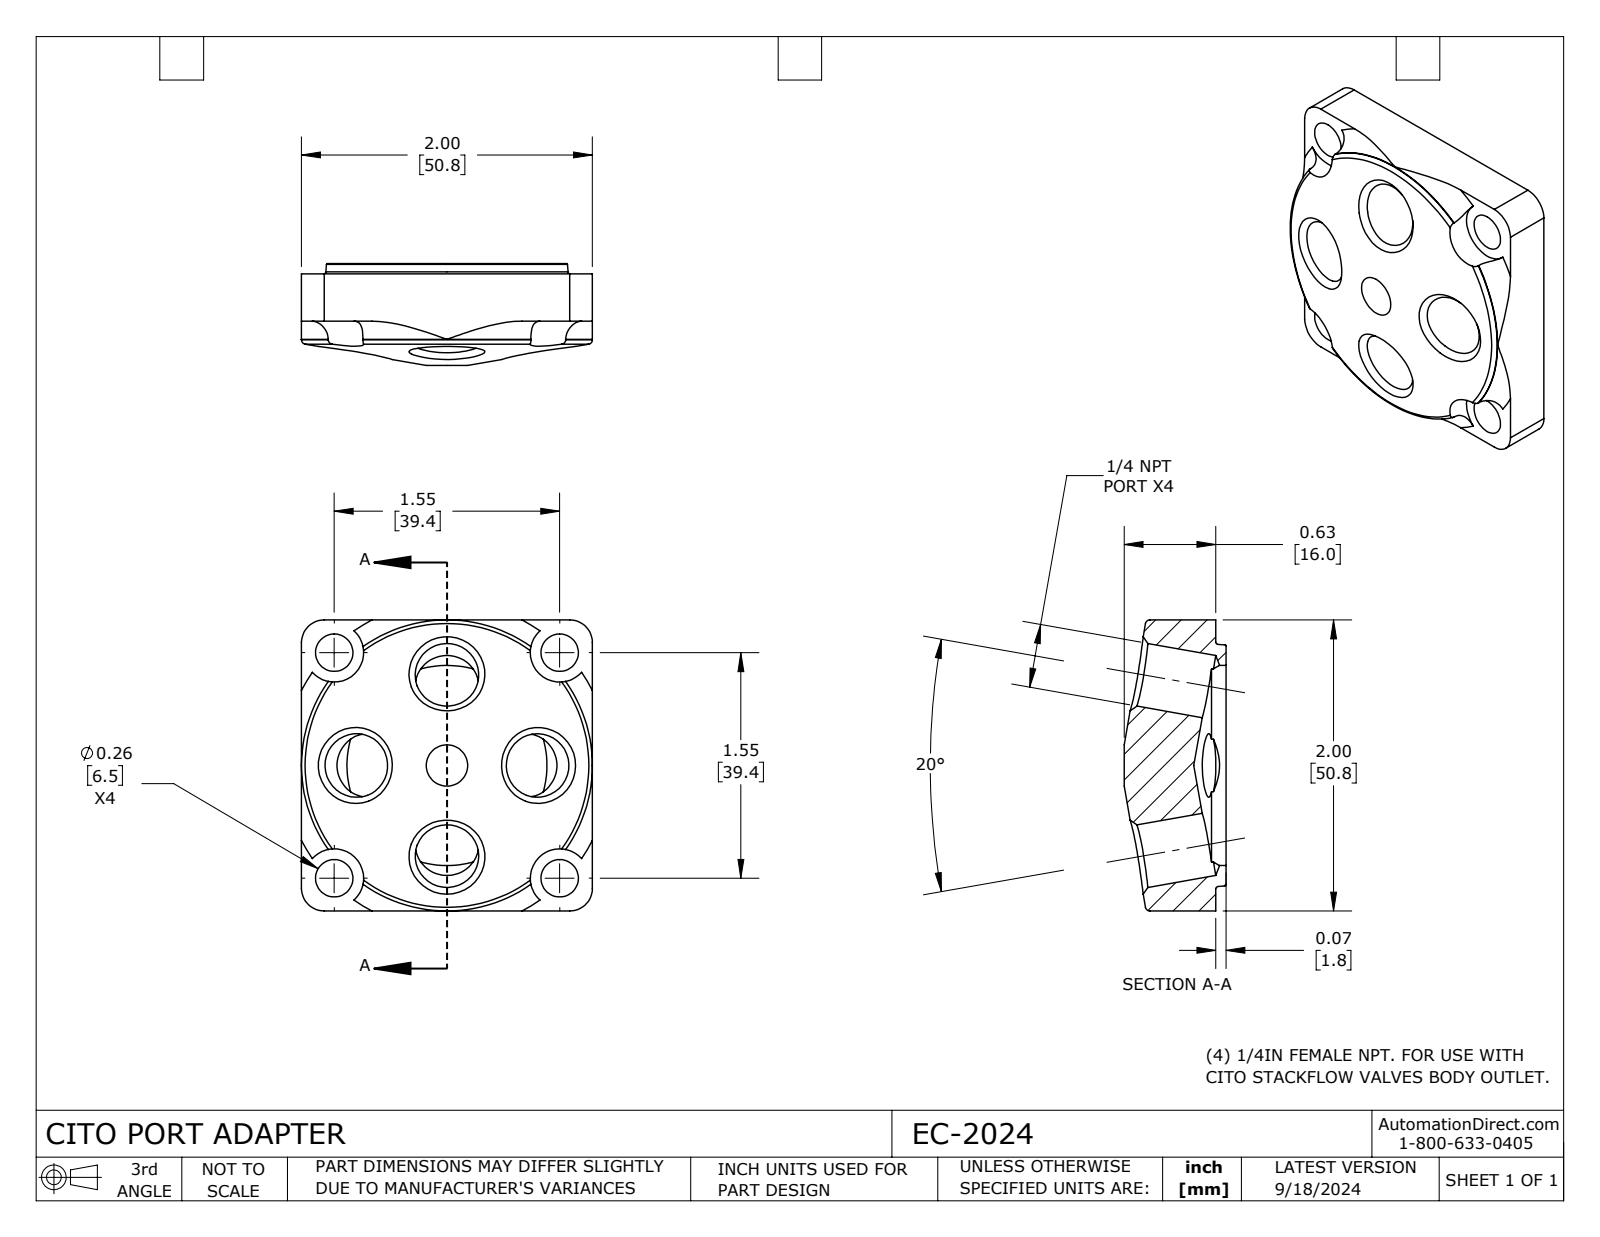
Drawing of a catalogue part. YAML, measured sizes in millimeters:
part_name: "EC-2024"
step_written_by: "SolidWorks 2023 (CONFIG_CONTROL_DESIGN)"
units: millimeters
bodies: {solids: 1, faces: 80, planar: 11, cylindrical: 33, other: 36}
overall_size: [50.8, 50.8, 17.8]
volume: 25010
surface_area: 9213
round_holes:
  - {diameter: 6.5, count: 4}
  - {diameter: 11.1, count: 4}
  - {diameter: 34.9, count: 1}
partial_cylinders:
  - {radius: 4, count: 4}
  - {radius: 5.1, count: 4}
  - {radius: 25.4, count: 1}
face_to_face_distances: [50.8, 1.8, 8.3, 10, 7.7, 16, 17.8]
hole_center_spacings: [27.8, 39.4, 55.7]
